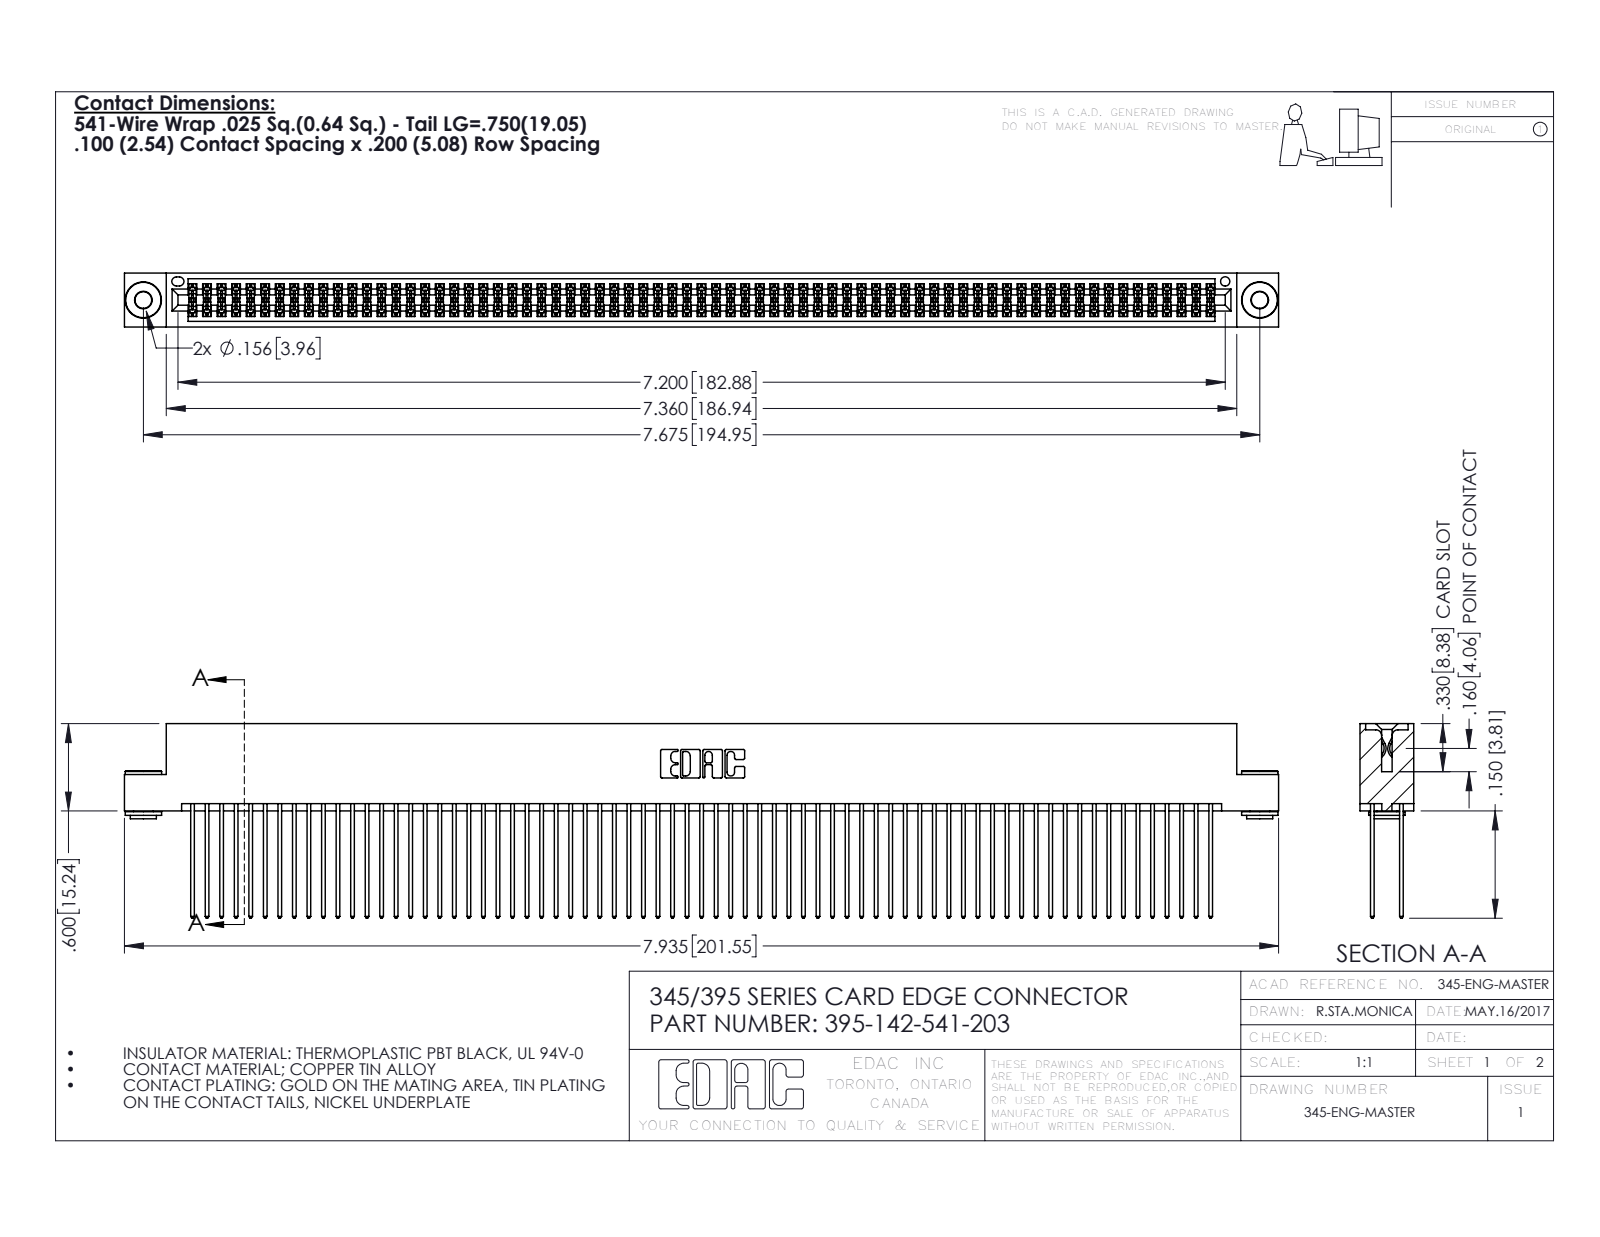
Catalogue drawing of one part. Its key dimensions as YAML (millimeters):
part_name: "345-292-001_345-293-141; 345-250-002_345-250-002-102; 345 Part_Flush Mounting Lugs - 0.156 Dia-TH; 395-142-541-203"
step_written_by: "SolidWorks 2016 (CONFIG_CONTROL_DESIGN)"
units: millimeters
bodies: {solids: 145, faces: 7264, planar: 4776, cylindrical: 2480, other: 8}
overall_size: [201.5, 34, 9.4]
volume: 20680
surface_area: 35170
round_holes:
  - {diameter: 2.9, count: 2}
  - {diameter: 4, count: 2}
  - {diameter: 1.6, count: 1}
round_bosses_or_shafts:
  - {diameter: 6.4, count: 2}
  - {diameter: 4.6, count: 2}
  - {diameter: 3.5, count: 2}
partial_cylinders:
  - {radius: 0.2, count: 213}
  - {radius: 0.3, count: 142}
  - {radius: 0.3, count: 22}
  - {radius: 0.2, count: 6}
  - {radius: 0.8, count: 6}
  - {radius: 0.7, count: 3}
  - {radius: 0.4, count: 2}
  - {radius: 0.5, count: 2}
face_to_face_distances: [1.8, 7.6, 5.1, 0.6, 2.5, 6.9, 5.7, 9.4, 4.4, 3.8]
hole_center_spacings: [6.9, 189, 194.9]
